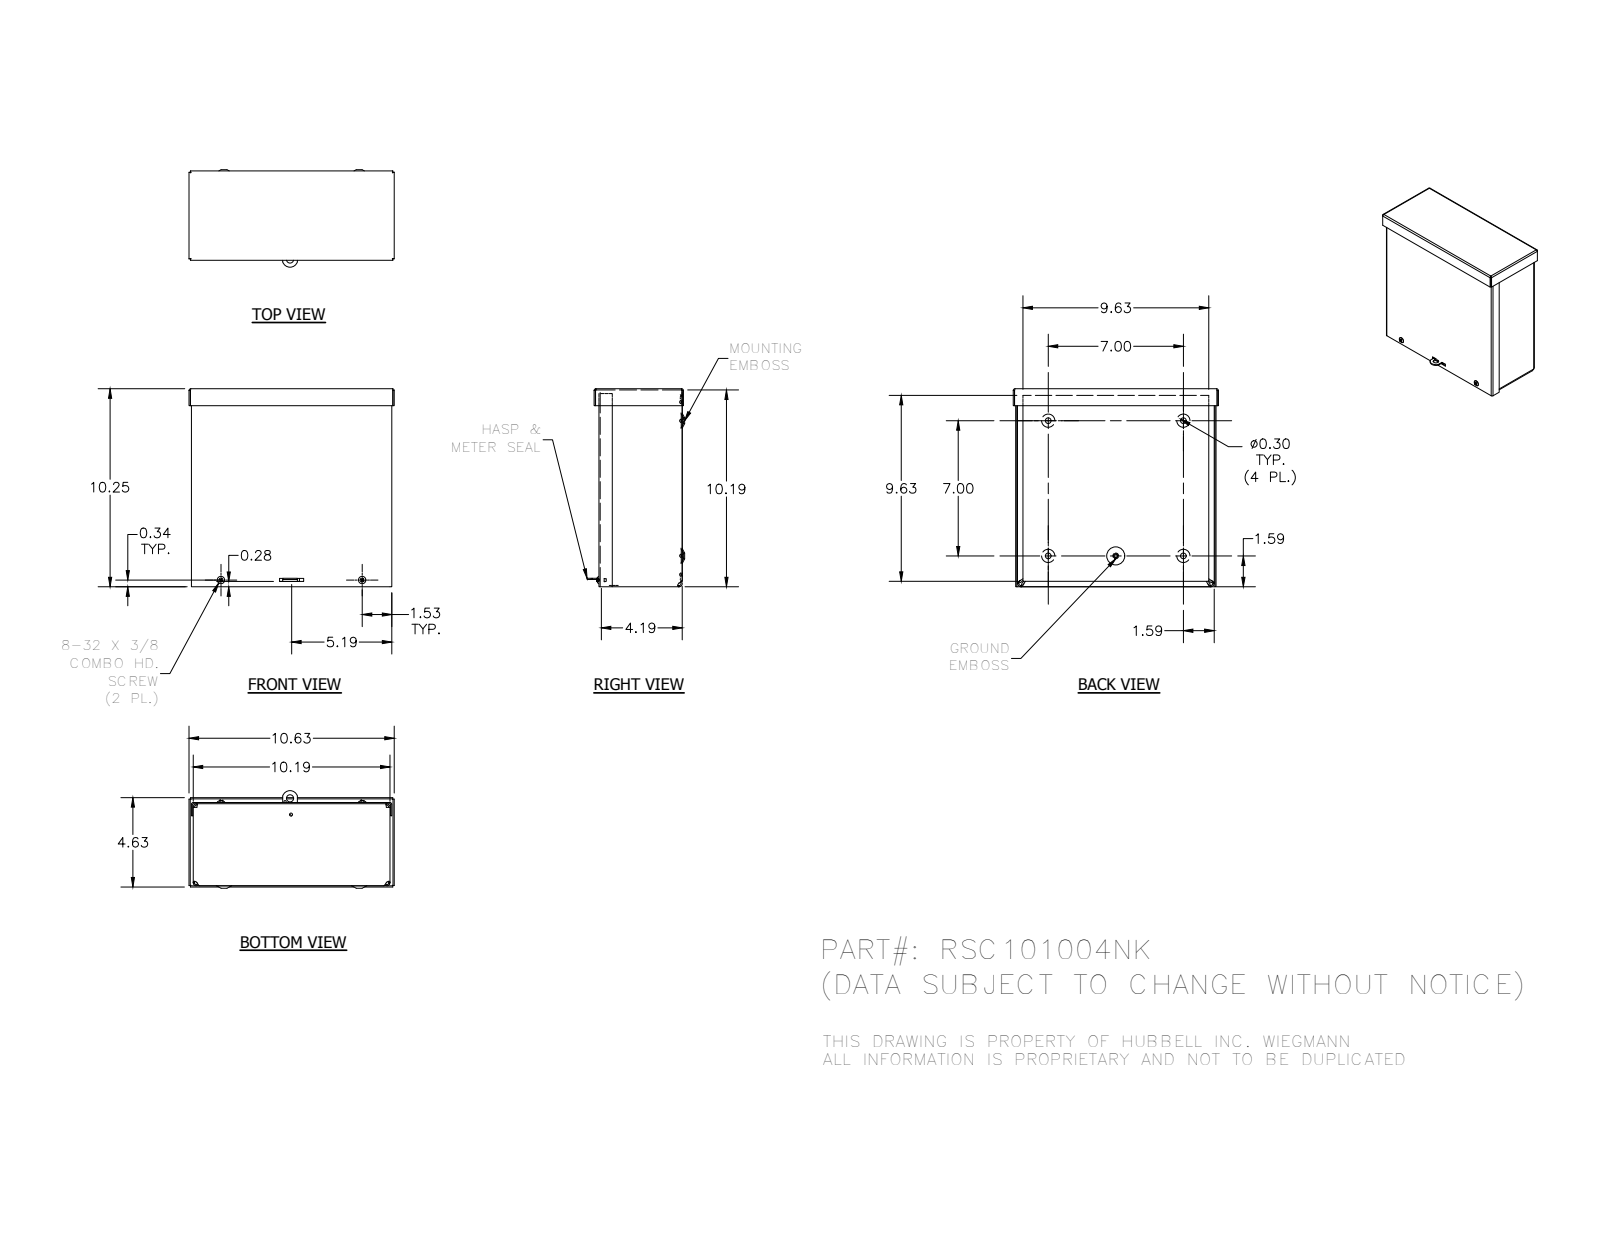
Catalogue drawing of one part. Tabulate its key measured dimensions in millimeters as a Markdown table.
| quantity | value |
| --- | --- |
| part name | RSC101004NK_WRAP; RSC1010NK_LID; RSC1004NK_CAP; 3183 (+3 more) |
| STEP written by | Autodesk Inventor 2014 (AUTOMOTIVE_DESIGN) |
| units | millimeters |
| bodies | 7 solids, 377 faces (163 planar, 78 cylindrical, 136 other) |
| overall size | 269.88 × 260.36 × 130.17 |
| volume | 514 354 mm³ |
| surface area | 662 276 mm² |
| round holes (diameter × count) | 7.62 × 4, 7.95 × 4, 3.76 × 2, 3.17 × 1, 3.45 × 1, 3.96 × 1, 4.19 × 1, 9.52 × 1 |
| round bosses / shafts (diameter × count) | 9.75 × 2, 4.17 × 2, 5.8 × 1 |
| partial cylindrical surfaces (radius × count) | 0.79 × 8, 2.37 × 8, 3.17 × 8, 4.75 × 8, 1.4 × 4, 1.57 × 4, 2.38 × 4, 2.97 × 4 |
| main face-to-face distances | 1.58, 257.19, 1.57, 107.93, 106.35, 1.59, 109.52, 107.94, 258.77, 3.15 |
| hole center spacings | 177.8, 27.24, 32.03, 88.9, 185.75, 198.78, 204.79, 209.62 |
